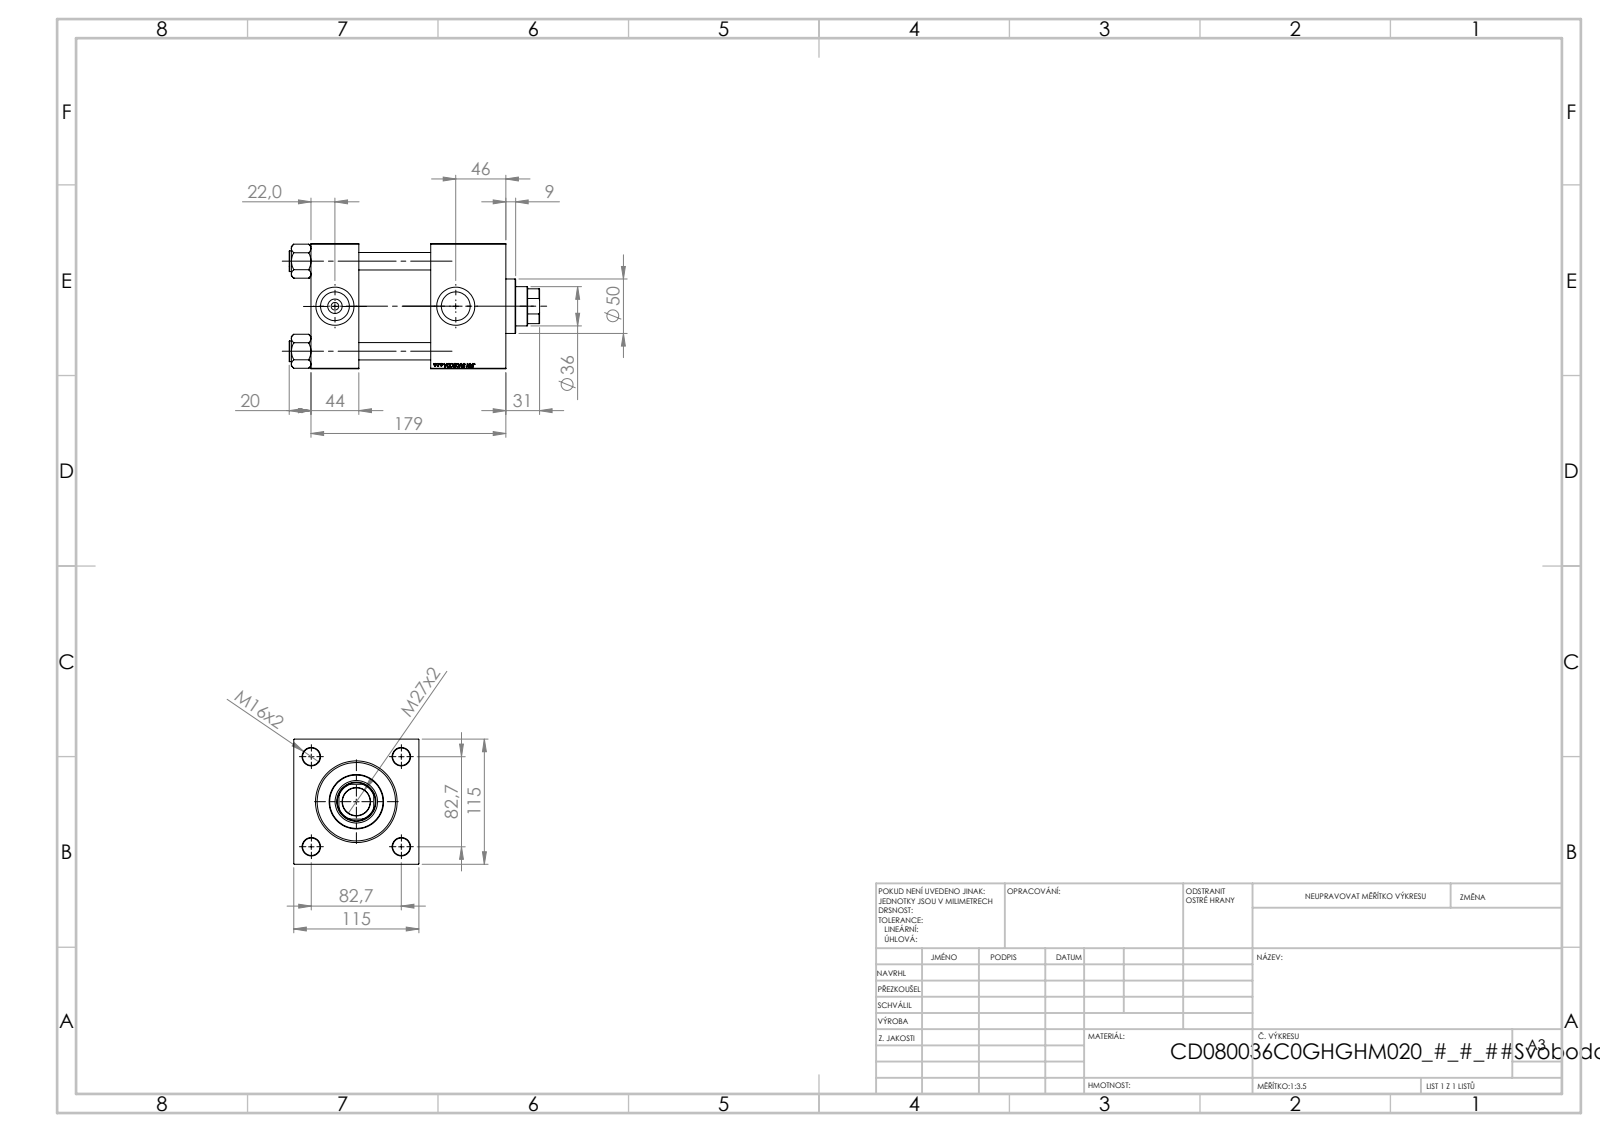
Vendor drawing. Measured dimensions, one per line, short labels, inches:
name: V215CD_VCP_C; V215CD_VC_C; V215CD_C_TYCINKA; NUT_M5_V215CD_C (+1 more)
written by: SolidWorks 2019 (CONFIG_CONTROL_DESIGN)
unit: in
bodies: 11 solids, 1196 faces (574 planar, 86 cylindrical, 536 other)
size: 9.055 × 4.528 × 4.528
volume: 109 in³; area: 416.1 in²
holes: 4× ⌀0.63, 2× ⌀0.276, 2× ⌀1.041, 2× ⌀1.378, 1× ⌀1.004, 1× ⌀1.417, 1× ⌀1.535, 1× ⌀2.402, 1× ⌀2.835, 1× ⌀3.15
bosses: 4× ⌀0.748, 1× ⌀3.386, 1× ⌀1.969
rounds: 1× R0.689
face distances: 4.528, 1.732, 7.047, 5.315, 4.331, 2.717, 2.598, 0.787, 5.917, 4.185
hole spacings: 2.302, 3.256, 4.605, 4.37
